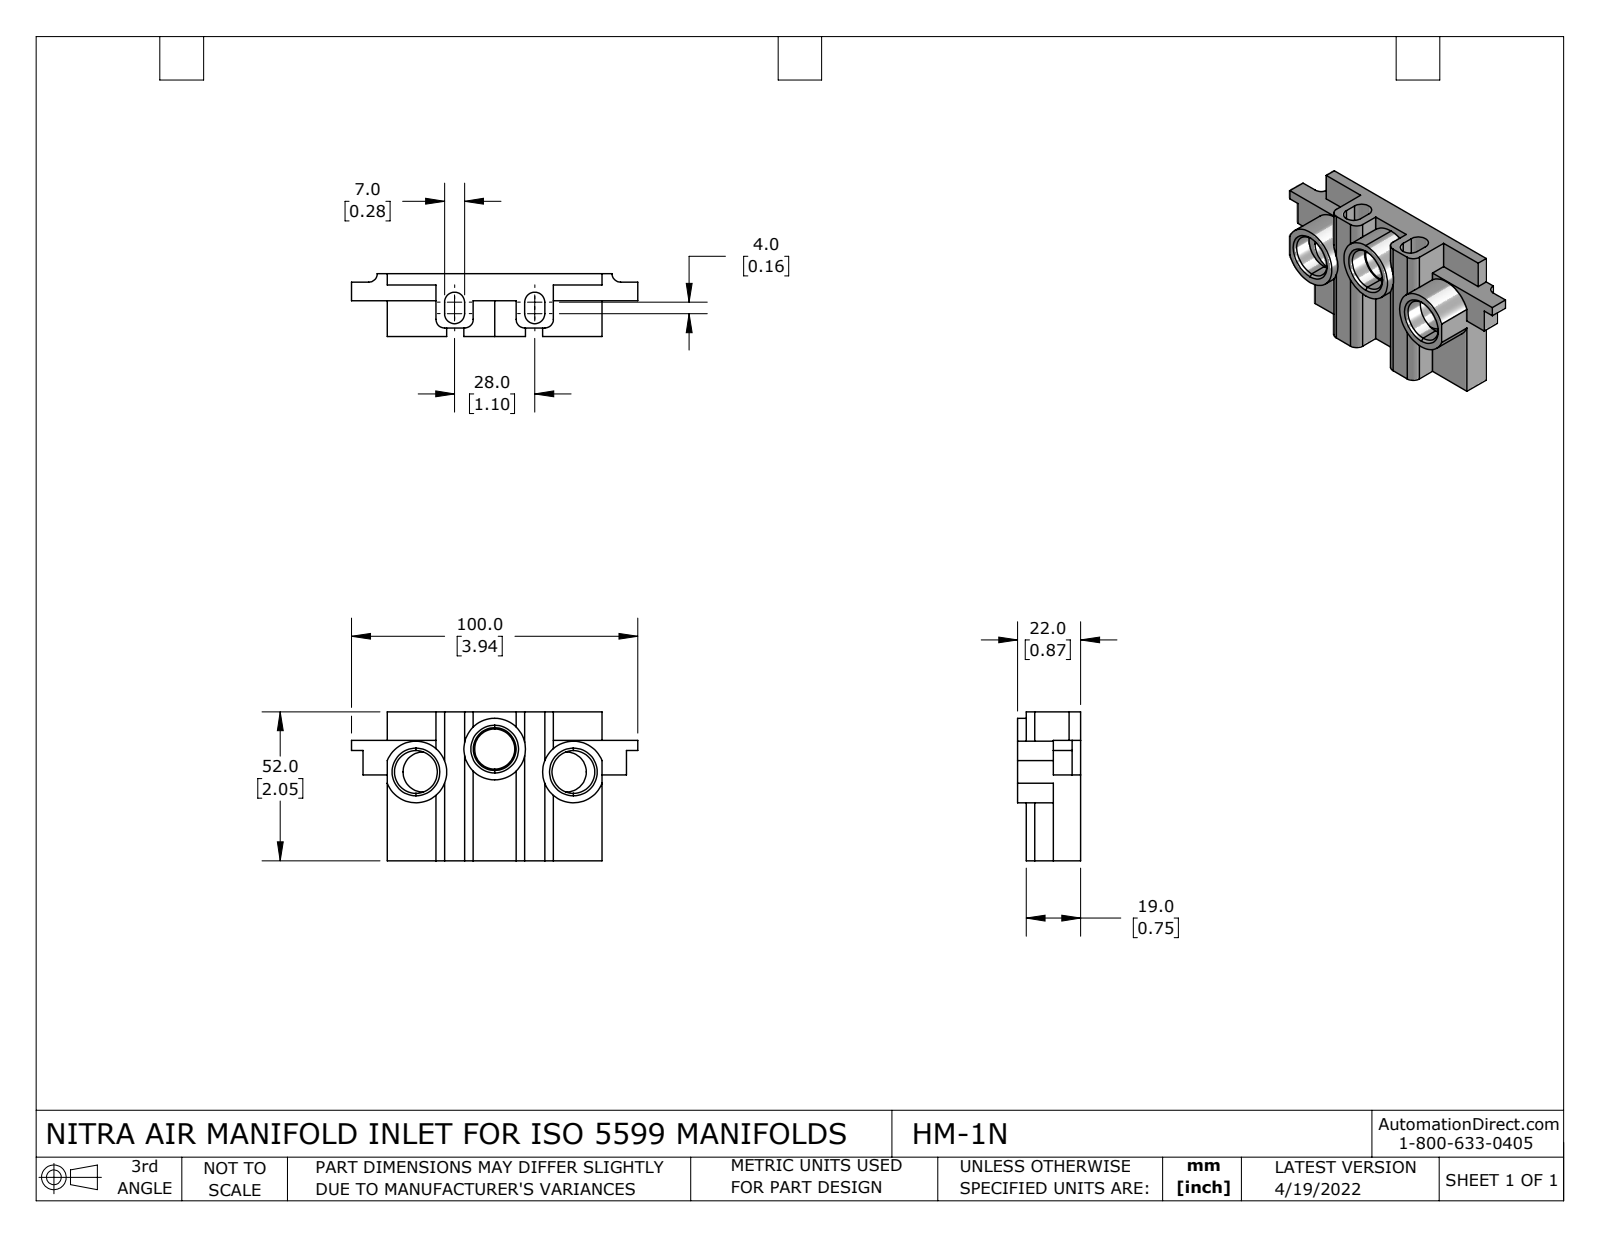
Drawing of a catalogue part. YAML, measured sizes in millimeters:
part_name: "HM-1N"
step_written_by: "SolidWorks 2021 (CONFIG_CONTROL_DESIGN)"
units: millimeters
bodies: {solids: 1, faces: 94, planar: 52, cylindrical: 36, other: 6}
overall_size: [100, 52, 22]
volume: 42844
surface_area: 19637
round_holes:
  - {diameter: 14, count: 3}
  - {diameter: 14.95, count: 3}
  - {diameter: 19, count: 3}
round_bosses_or_shafts:
  - {diameter: 21.5, count: 3}
partial_cylinders:
  - {radius: 3, count: 6}
  - {radius: 3.5, count: 4}
face_to_face_distances: [9.5, 3, 10, 19, 28, 18, 15, 52, 30, 7]
hole_center_spacings: [2.5, 26.25, 28.64, 52.5, 50, 55]
